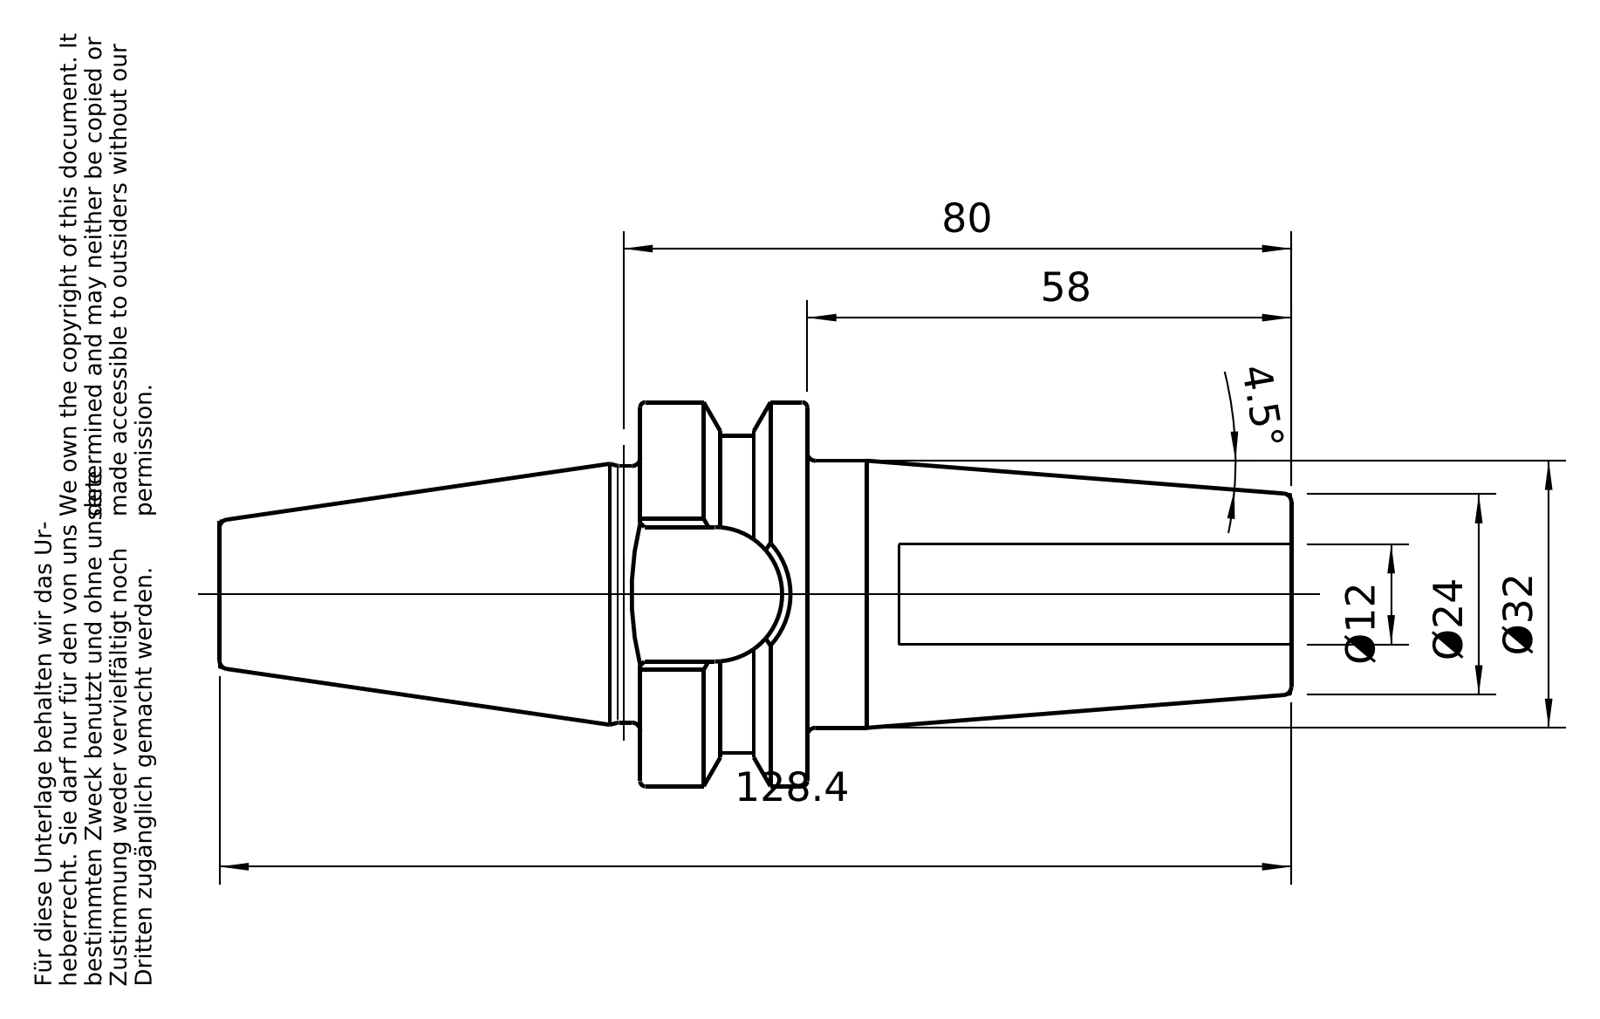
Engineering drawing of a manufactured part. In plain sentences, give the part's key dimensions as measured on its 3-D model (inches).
The part is named "30-640-12". Its 3-D file was written by "PRO/ENGINEER BY PARAMETRIC TECHNOLOGY CORPORATION, 2010430 (CONFIG_CONTROL_DESIGN)". It is 1 solid with 96 faces: 26 planar, 22 cylindrical and 48 other. Overall it measures 5.055 by 1.81 by 1.81 inches. Its volume is 4.973 cubic inches and its surface area 28.52 square inches. Round holes: 1 of diameter 0.398, 1 of diameter 0.472, 1 of diameter 0.493, 1 of diameter 0.512. Round bosses or shafts: 1 of diameter 1.81, 1 of diameter 1.26, 1 of diameter 1.211, 1 of diameter 0.473. Partial cylindrical surfaces (rounded edges, fillets, slot ends): 1 of radius 0.319, 1 of radius 0.743. The main face-to-face distances are 0.787, 3.071, 2.283, 1.272, 1.22, 0.433, 1.85, 0.638, 1.984, 2.772.
